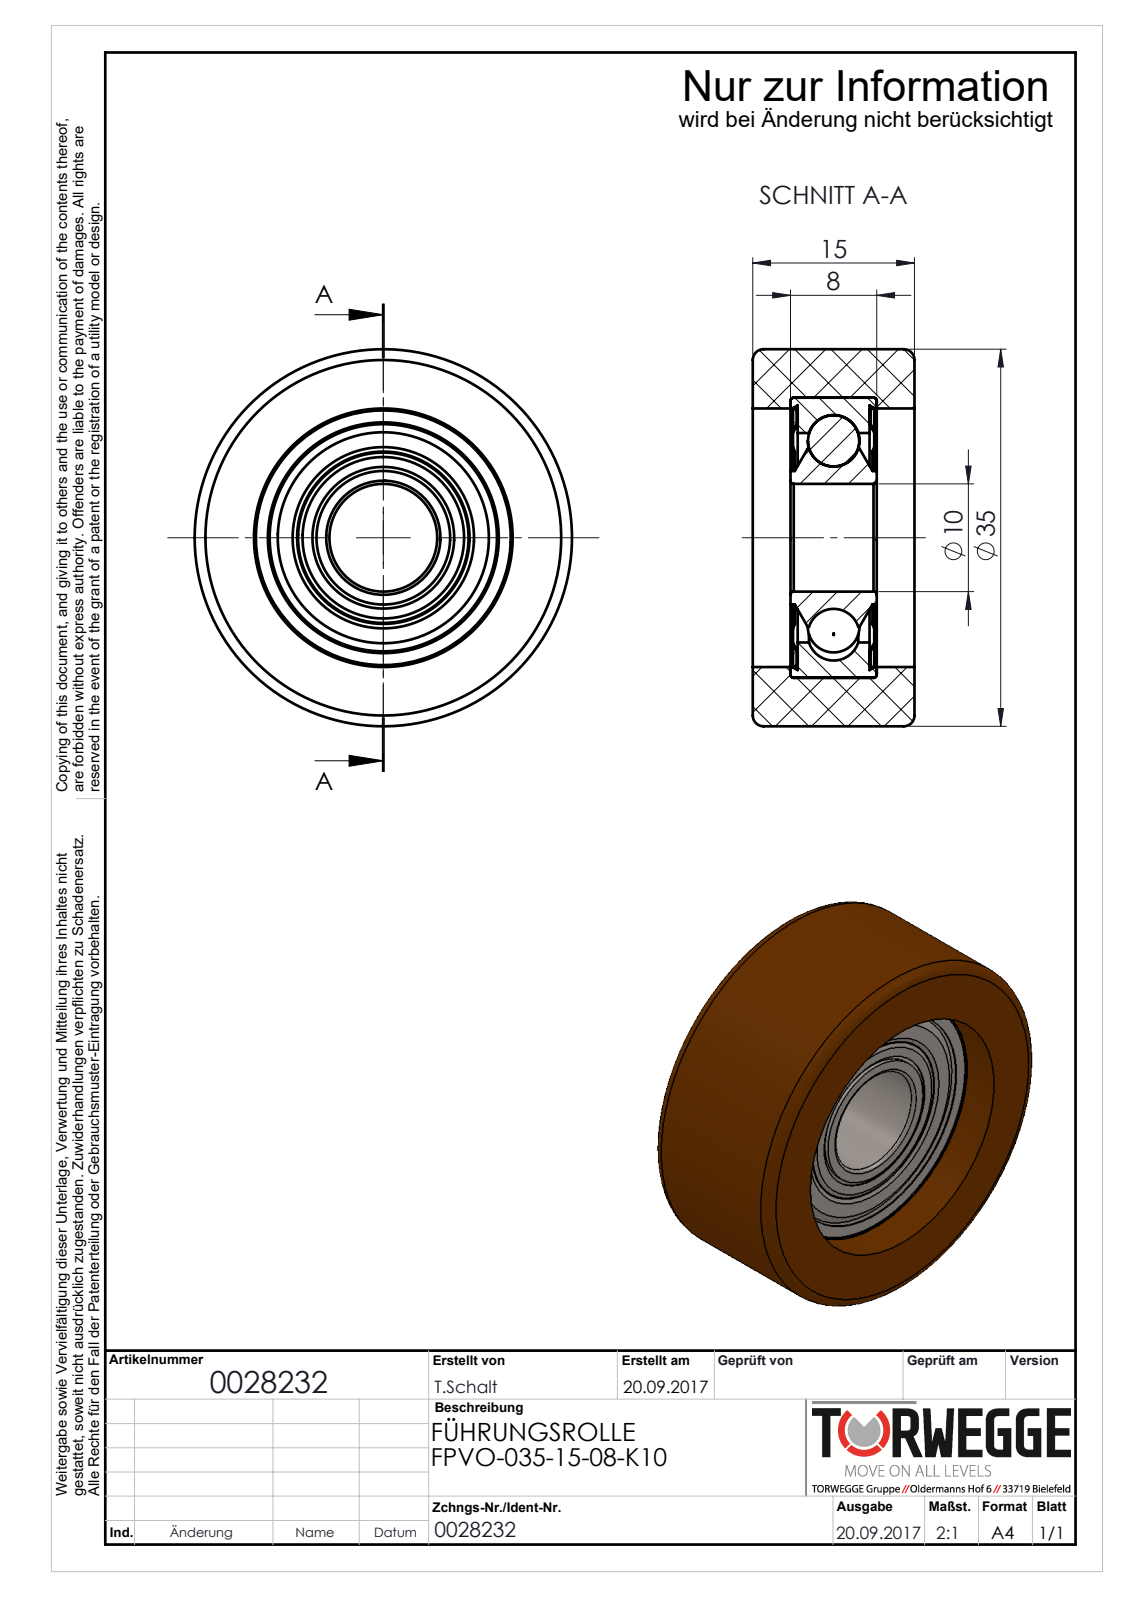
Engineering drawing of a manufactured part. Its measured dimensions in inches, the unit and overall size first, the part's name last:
Units: inches
Overall size (bounding box): 1.378 × 1.378 × 0.591
Round holes (diameter × count): ⌀0.394 ×1, ⌀0.518 ×1, ⌀0.765 ×1, ⌀0.843 ×1, ⌀0.945 ×1, ⌀1.024 ×1
Round bosses / shafts (diameter × count): ⌀1.378 ×1, ⌀0.652 ×1, ⌀0.488 ×1
Main face-to-face distances: 0.283, 0.017, 0.591, 0.021, 0.3, 0.28, 0.138, 0.453, 0.164, 0.426
Volume: 0.573 in³ · Surface area: 13.76 in²
Bodies: 6 solids, 160 faces (30 planar, 32 cylindrical, 98 other)
Part name (STEP PRODUCT): FPVO-035-15-08-K10_Bandage; 0028232_FPVO-035-15-08-K10; Rillenkugellager_DIN625-6000-ZZ
STEP written by: SolidWorks 2016 (AUTOMOTIVE_DESIGN)
